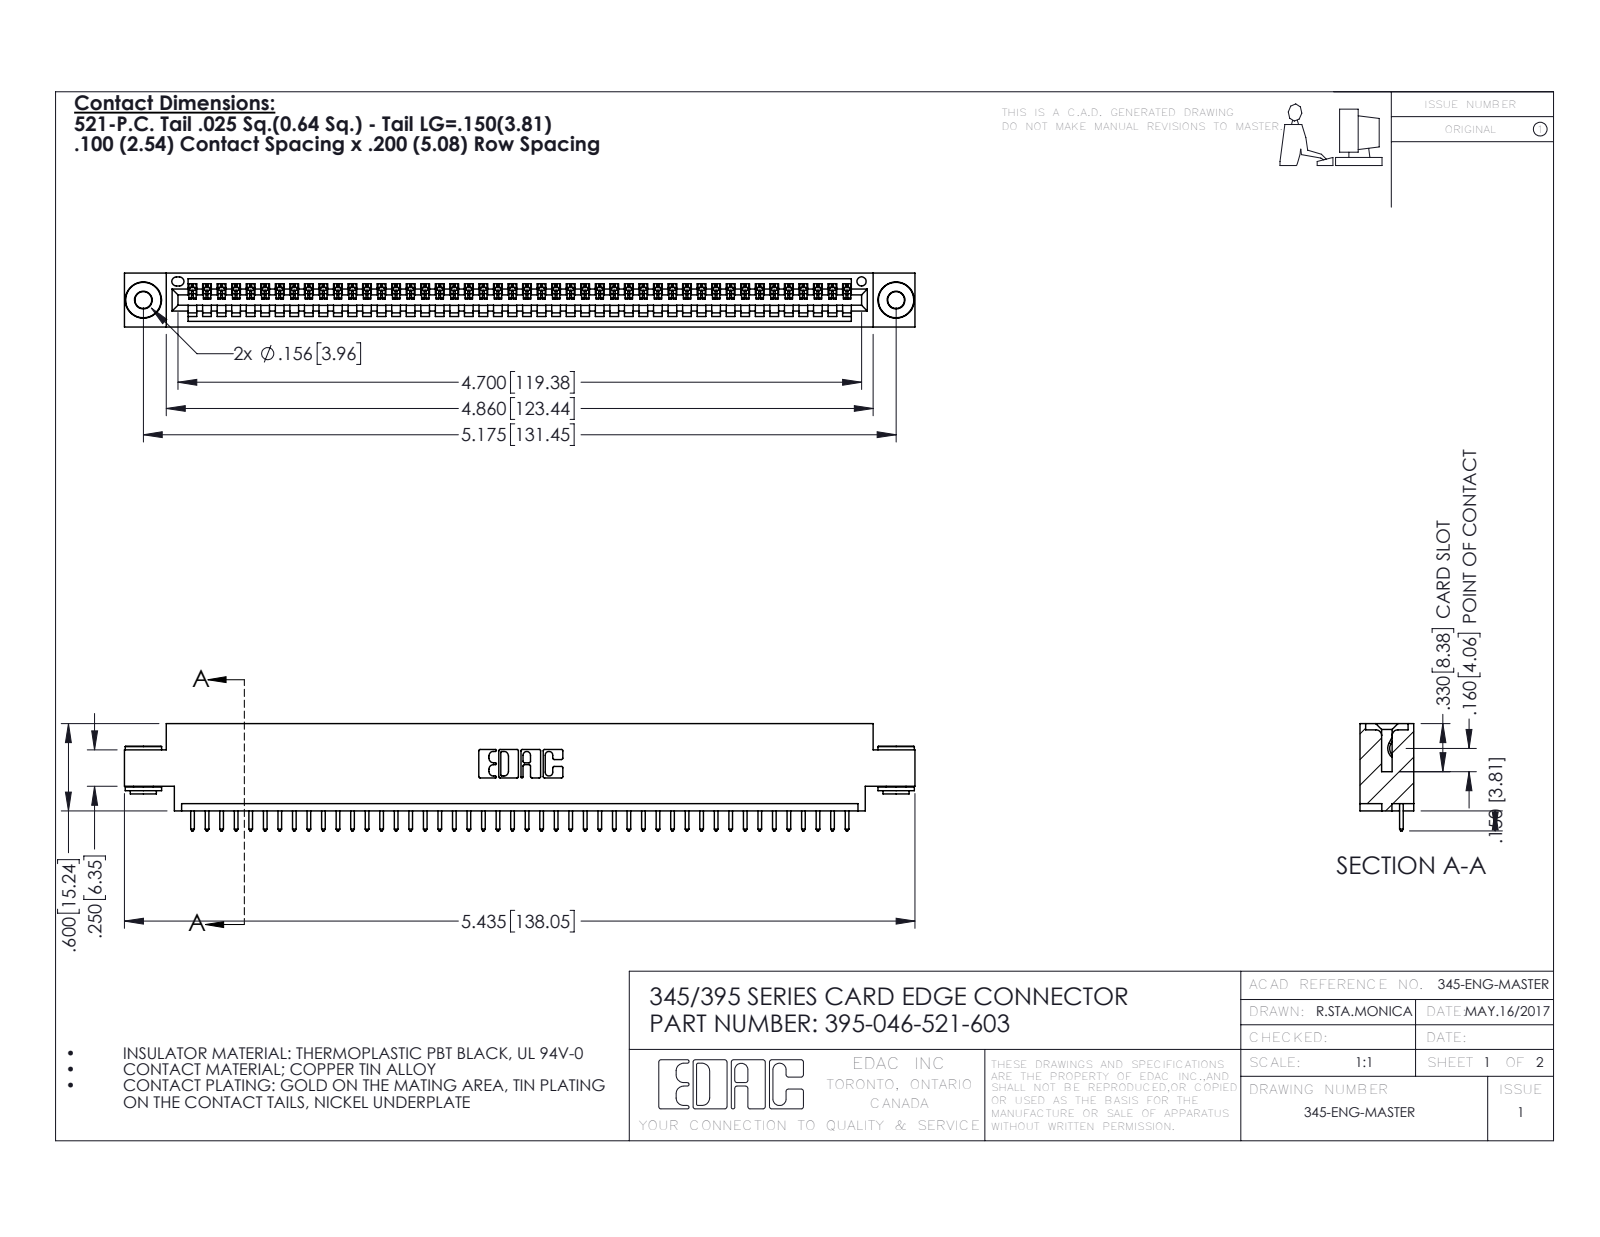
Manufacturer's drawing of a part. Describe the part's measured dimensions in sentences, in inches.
The part is named "345-292-001_345-293-121; 345-250-002_345-250-002-102; 395-046-521-603; 345 Part_0.170 Offset - 0.156 Dia-TH". Its 3-D file was written by "SolidWorks 2016 (CONFIG_CONTROL_DESIGN)". It is 49 solids with 2836 faces: 1934 planar, 894 cylindrical and 8 other. Overall it measures 5.435 by 0.737 by 0.37 inches. Its volume is 0.788 cubic inches and its surface area 26.43 square inches. Round holes: 2 of diameter 0.116, 2 of diameter 0.156, 1 of diameter 0.064. Round bosses or shafts: 2 of diameter 0.25, 2 of diameter 0.18, 2 of diameter 0.136. Partial cylindrical surfaces (rounded edges, fillets, slot ends): 92 of radius 0.006, 92 of radius 0.01, 22 of radius 0.01, 6 of radius 0.007, 6 of radius 0.031, 3 of radius 0.026, 2 of radius 0.031, 2 of radius 0.04. The main face-to-face distances are 0.072, 0.298, 0.37, 0.2, 0.098, 0.272, 0.025, 0.225, 0.175, 0.149. The hole center spacings are 0.27, 4.939, 5.175.
